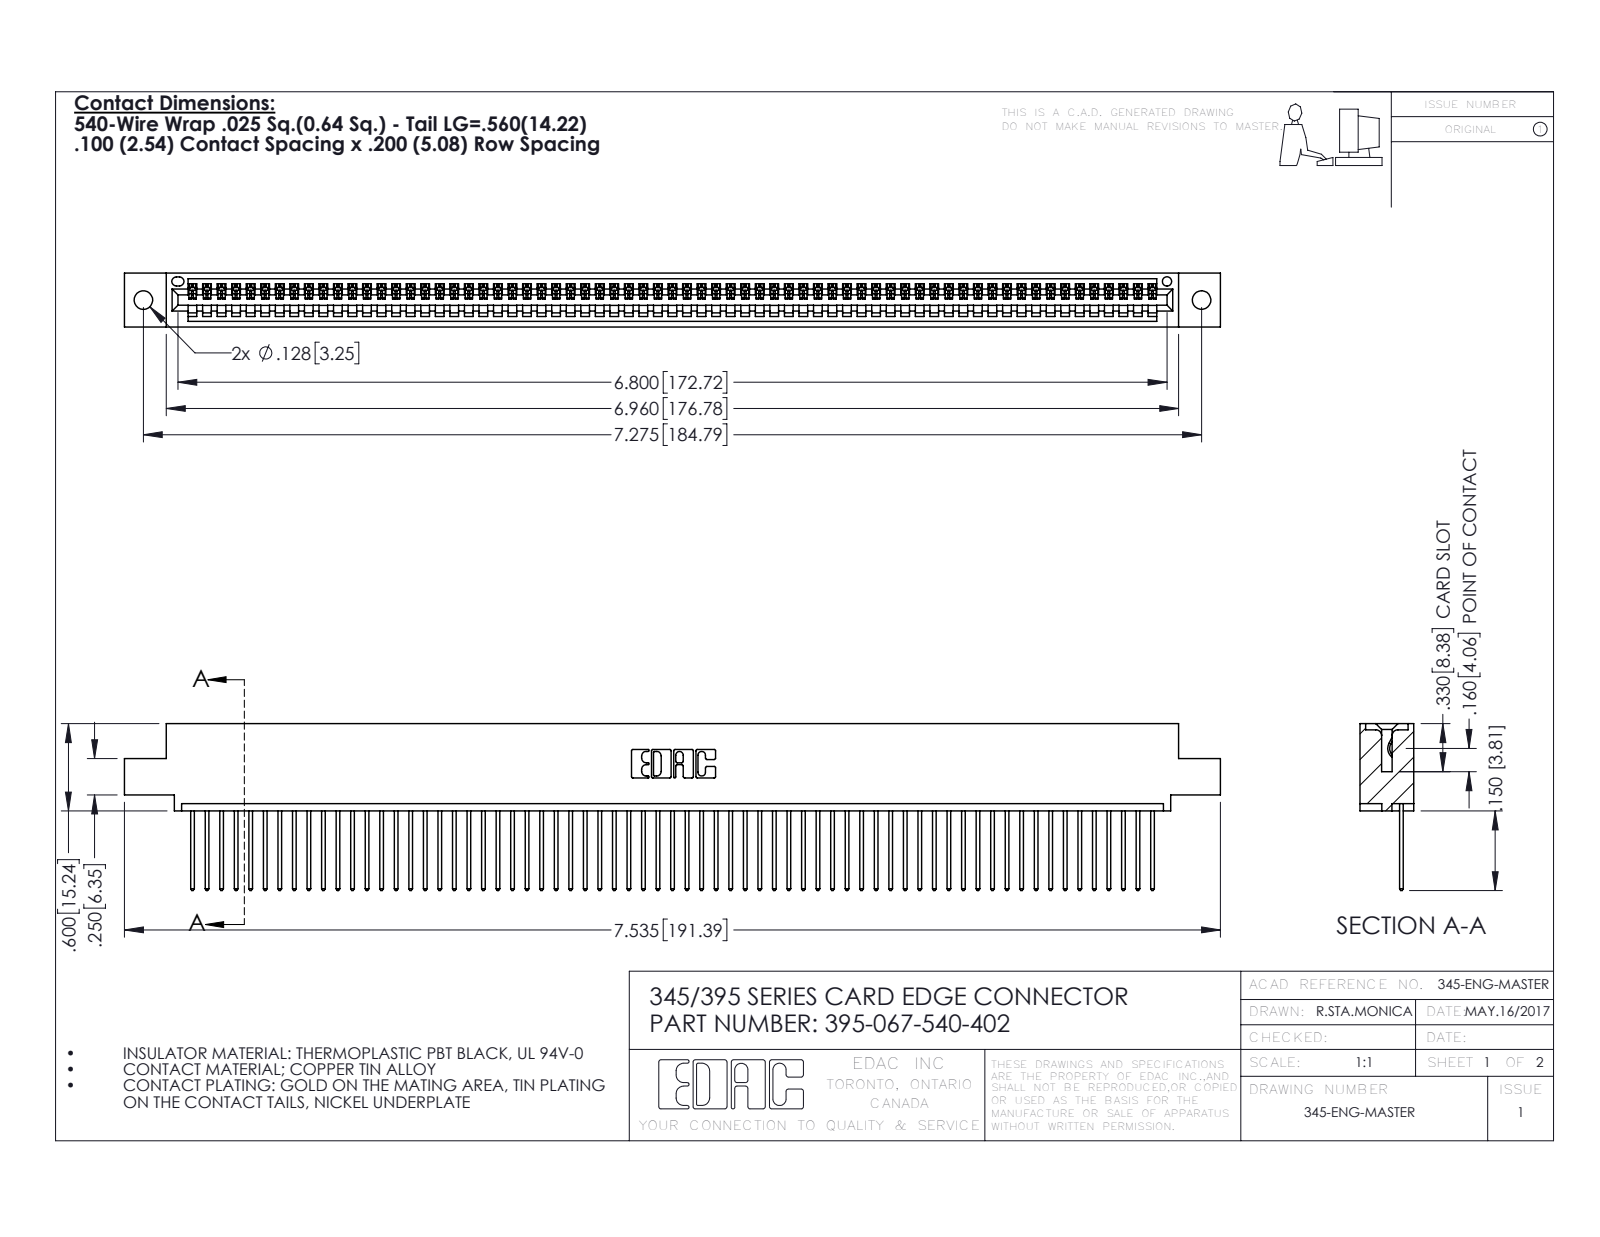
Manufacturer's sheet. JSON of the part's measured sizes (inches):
{"part_name": "345 Part_0.110 Offset - 0.128 Dia; 395-067-540-402; 345-292-001_345-293-140", "step_written_by": "SolidWorks 2016 (CONFIG_CONTROL_DESIGN)", "units": "inches", "bodies": {"solids": 68, "faces": 4016, "planar": 2764, "cylindrical": 1252, "other": 0}, "overall_size": [7.535, 1.147, 0.37], "volume_in3": 1.121, "surface_area_in2": 39.07, "round_holes": [[0.128, 2], [0.064, 1]], "partial_cylinders_radius": [[0.006, 134], [0.01, 134], [0.01, 22], [0.007, 6], [0.031, 6], [0.026, 3], [0.031, 2], [0.04, 2]], "face_to_face_distances": [0.072, 0.298, 0.37, 0.098, 0.272, 0.025, 0.2, 0.225, 0.149, 0.072], "hole_center_spacings": [0.27, 7.039, 7.275]}
